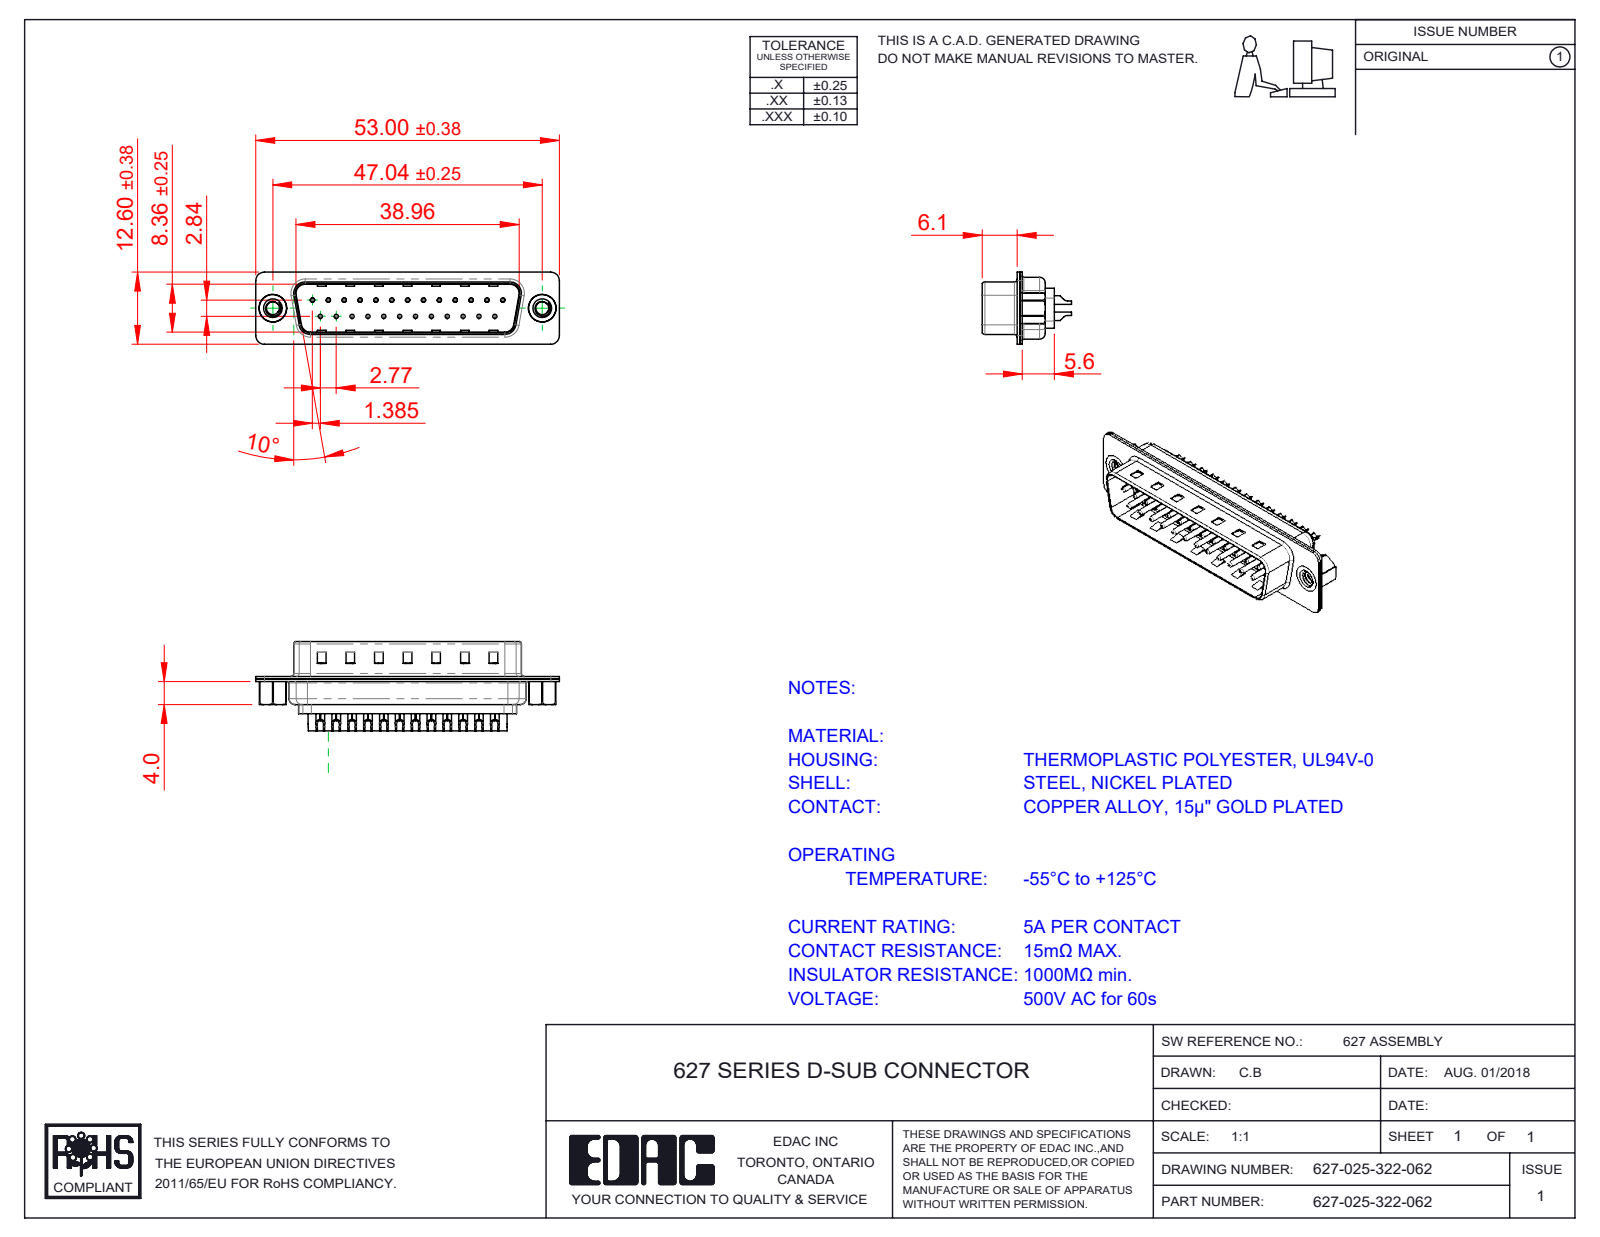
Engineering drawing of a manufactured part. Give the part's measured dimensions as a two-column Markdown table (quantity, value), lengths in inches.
| quantity | value |
| --- | --- |
| part name | 627-025-322-062; 627 4-40 Threaded Rivet; 627 Shell Rear_25 Contacts; 627 Contact Row 2_22L (+3 more) |
| STEP written by | SolidWorks 2020 (CONFIG_CONTROL_DESIGN) |
| units | inches |
| bodies | 30 solids, 1972 faces (521 planar, 860 cylindrical, 591 other) |
| overall size | 2.087 × 0.604 × 0.496 |
| volume | 0.164 in³ |
| surface area | 12.16 in² |
| round holes (diameter × count) | 0.014 × 25, 0.043 × 25, 0.063 × 25, 0.089 × 2, 0.157 × 2, 0.189 × 2 |
| round bosses / shafts (diameter × count) | 0.079 × 25, 0.059 × 25, 0.03 × 25, 0.197 × 2, 0.193 × 2 |
| partial cylindrical surfaces (radius × count) | 0.059 × 16, 0.079 × 12, 0.02 × 8, 0.063 × 8, 0.039 × 6, 0.01 × 4, 0.024 × 4, 0.026 × 4 |
| main face-to-face distances | 0.016, 0.018, 0.032, 0.377, 0.345, 0.035, 0.059, 0.055, 0.256, 0.238 |
| hole center spacings | 0.124, 0.327, 0.109, 0.218, 0.436, 0.654, 0.198, 0.198 |
